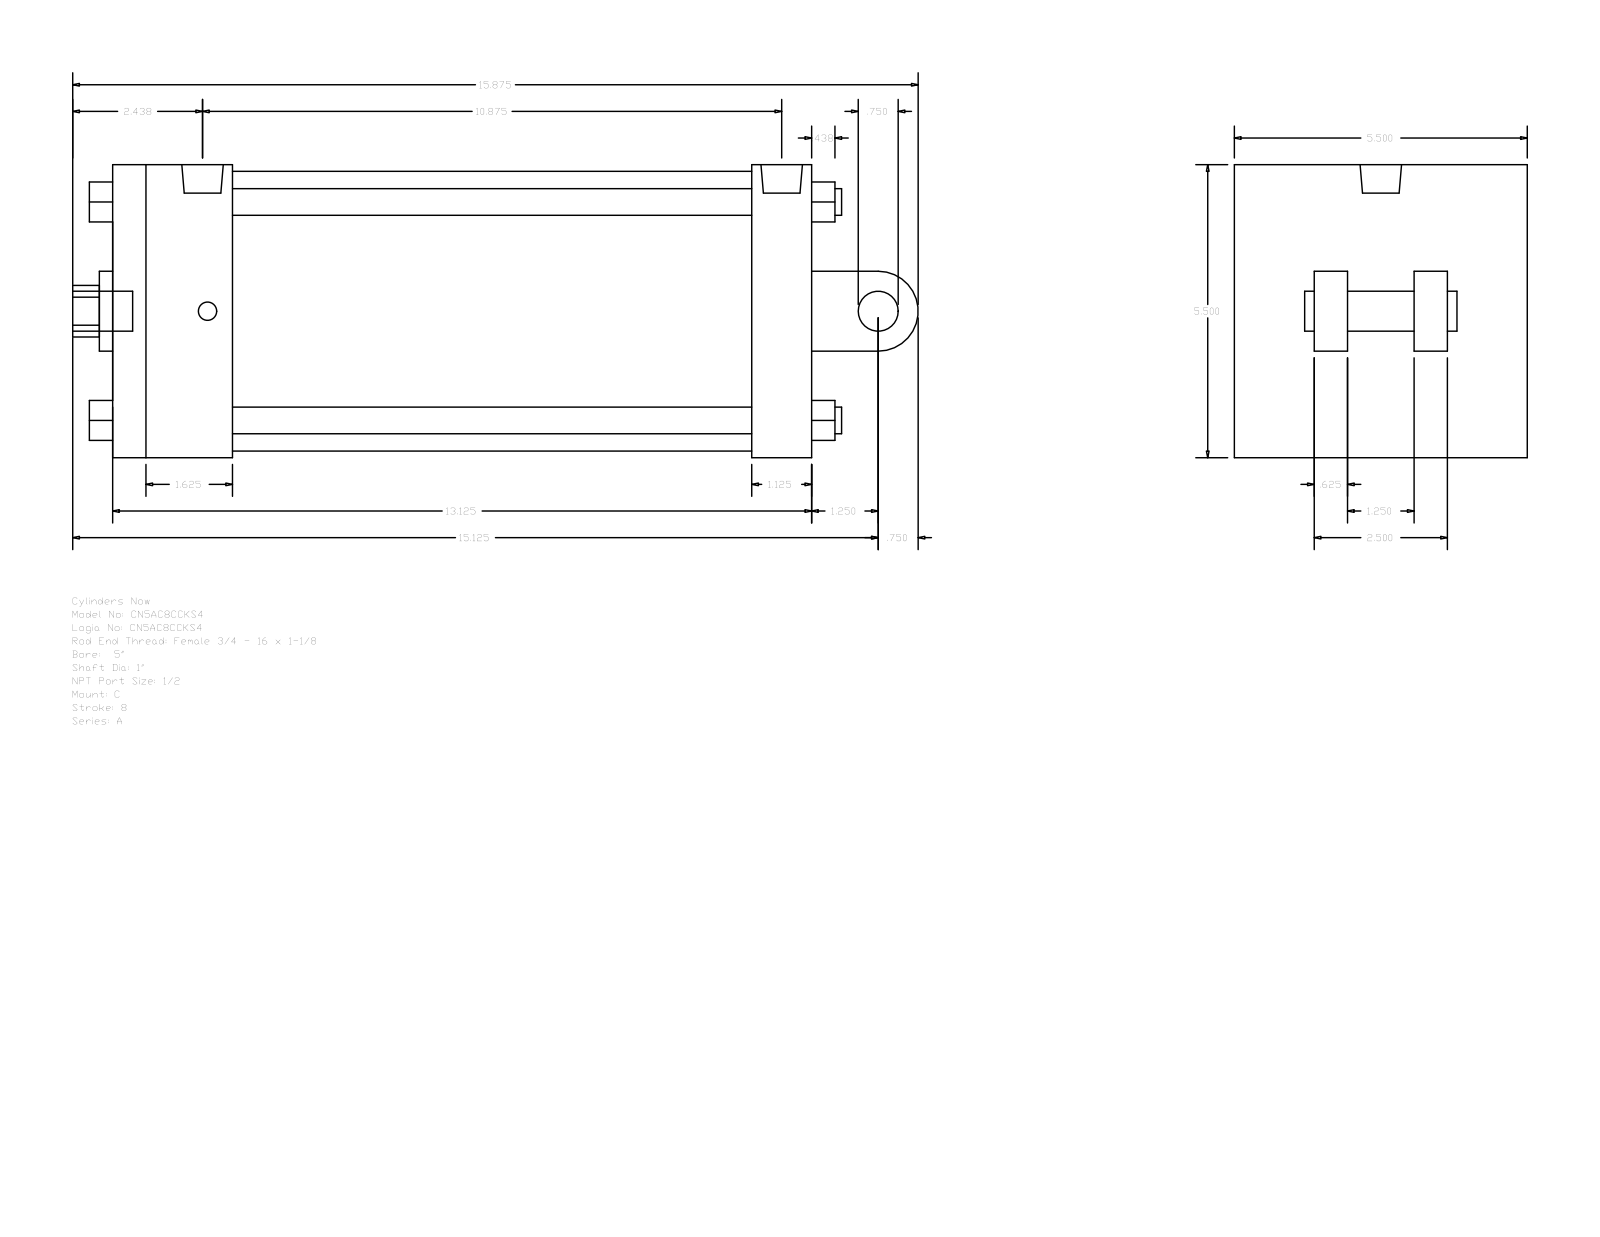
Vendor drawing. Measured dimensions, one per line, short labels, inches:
name: A_C__0500_1
written by: GSSL Pune (CONFIG_CONTROL_DESIGN)
unit: in
bodies: 0 solids, 135 faces (102 planar, 33 cylindrical, 0 other)
size: 15.875 × 5.5 × 5.5
holes: 2× ⌀0.344, 1× ⌀0.778, 1× ⌀1, 1× ⌀1.5, 1× ⌀5.25
bosses: 4× ⌀0.5, 2× ⌀0.75, 2× ⌀0.344, 1× ⌀0.778
rounds: 1× R0.484, 1× R0.75
face distances: 5.5, 13.125, 2.25, 12, 9.75, 10.875, 1.125, 1.5, 0.625, 1.875
hole spacings: 0.094
